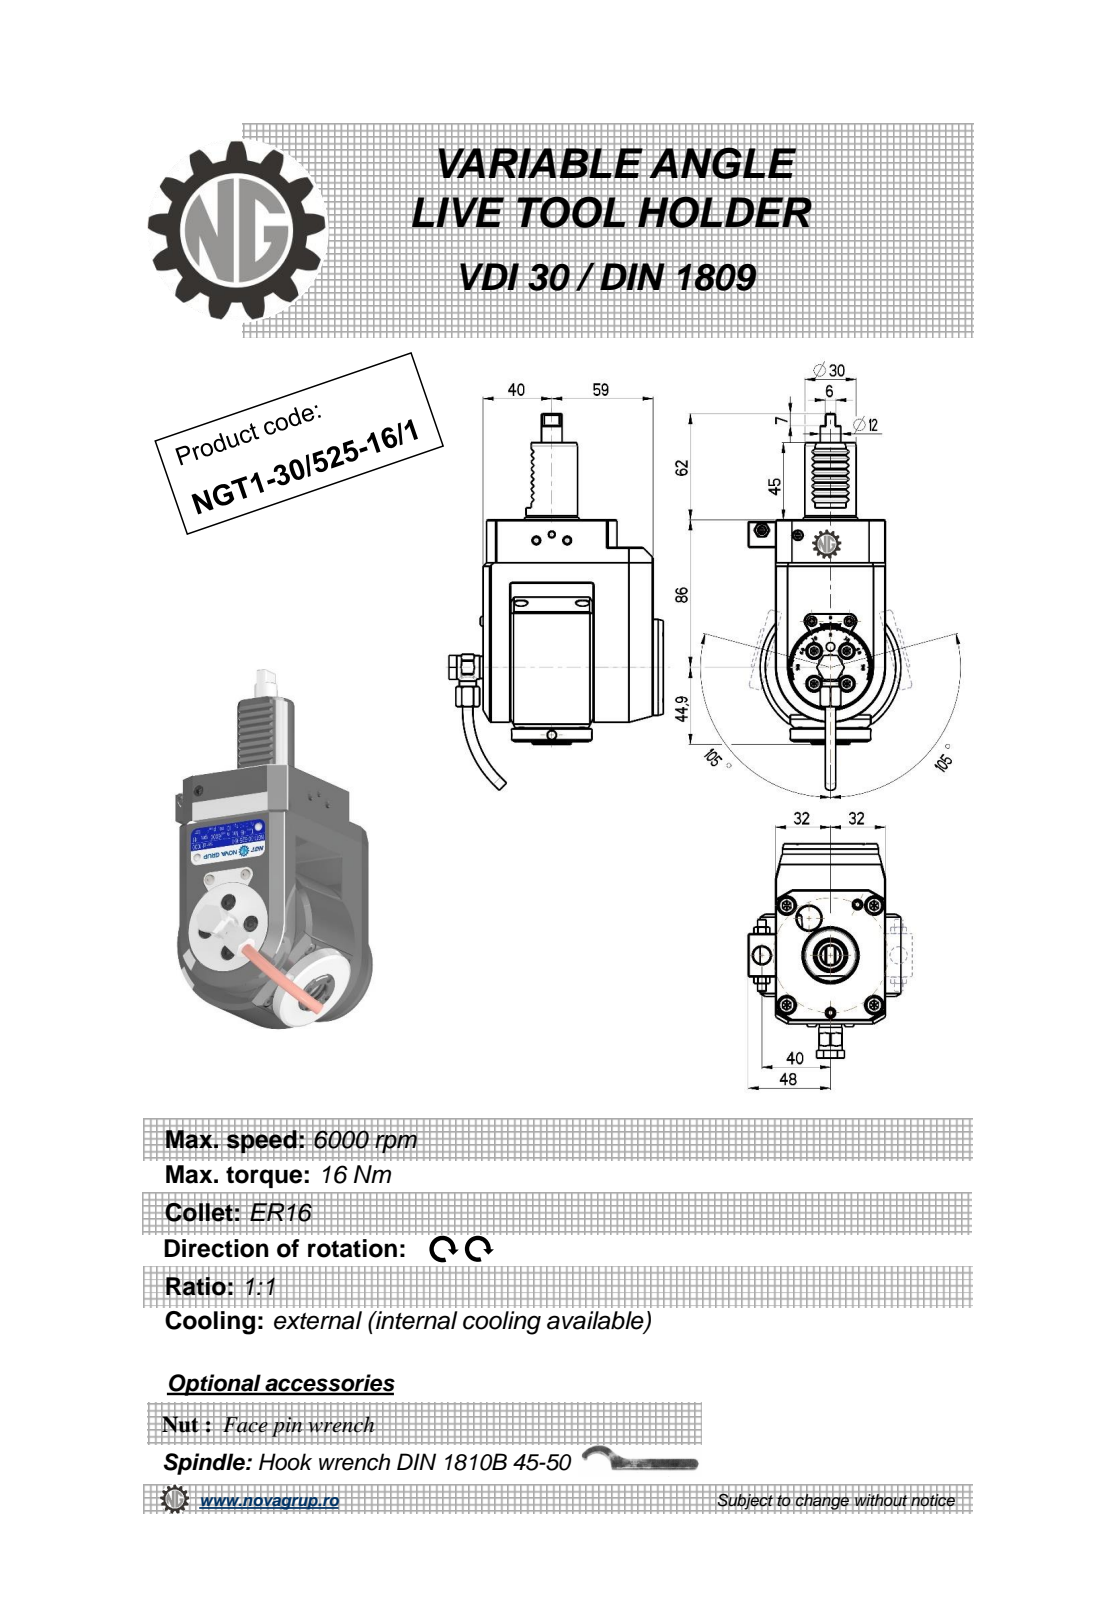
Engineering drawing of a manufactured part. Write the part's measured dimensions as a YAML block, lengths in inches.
part_name: "NGT1_30_525_16_1"
step_written_by: "PRO/ENGINEER BY PARAMETRIC TECHNOLOGY CORPORATION, 2010280 (CONFIG_CONTROL_DESIGN)"
units: inches
bodies: {solids: 1, faces: 481, planar: 202, cylindrical: 132, other: 147}
overall_size: [8.648, 4.917, 3.504]
volume: 45.98
surface_area: 109.4
round_holes:
  - {diameter: 0.126, count: 4}
  - {diameter: 0.157, count: 3}
  - {diameter: 0.197, count: 2}
  - {diameter: 0.394, count: 2}
  - {diameter: 0.118, count: 1}
  - {diameter: 0.165, count: 1}
  - {diameter: 0.244, count: 1}
  - {diameter: 0.354, count: 1}
  - {diameter: 0.374, count: 1}
  - {diameter: 0.433, count: 1}
  - {diameter: 0.492, count: 1}
round_bosses_or_shafts:
  - {diameter: 0.236, count: 2}
  - {diameter: 0.224, count: 2}
  - {diameter: 3.228, count: 1}
  - {diameter: 2.205, count: 1}
  - {diameter: 1.85, count: 1}
  - {diameter: 1.378, count: 1}
  - {diameter: 1.181, count: 1}
  - {diameter: 0.906, count: 1}
partial_cylinders:
  - {radius: 0.01, count: 12}
  - {radius: 0.012, count: 8}
  - {radius: 0.006, count: 6}
  - {radius: 0.02, count: 6}
  - {radius: 0.039, count: 2}
  - {radius: 0.303, count: 1}
  - {radius: 1.26, count: 1}
face_to_face_distances: [2.52, 0.63, 1.457, 3.898, 0.236, 4.134, 1.378, 0.827, 0.551, 3.268]
hole_center_spacings: [0.364, 0.515, 0.728, 1.617, 1.963, 1.979, 0.016, 1.211]
